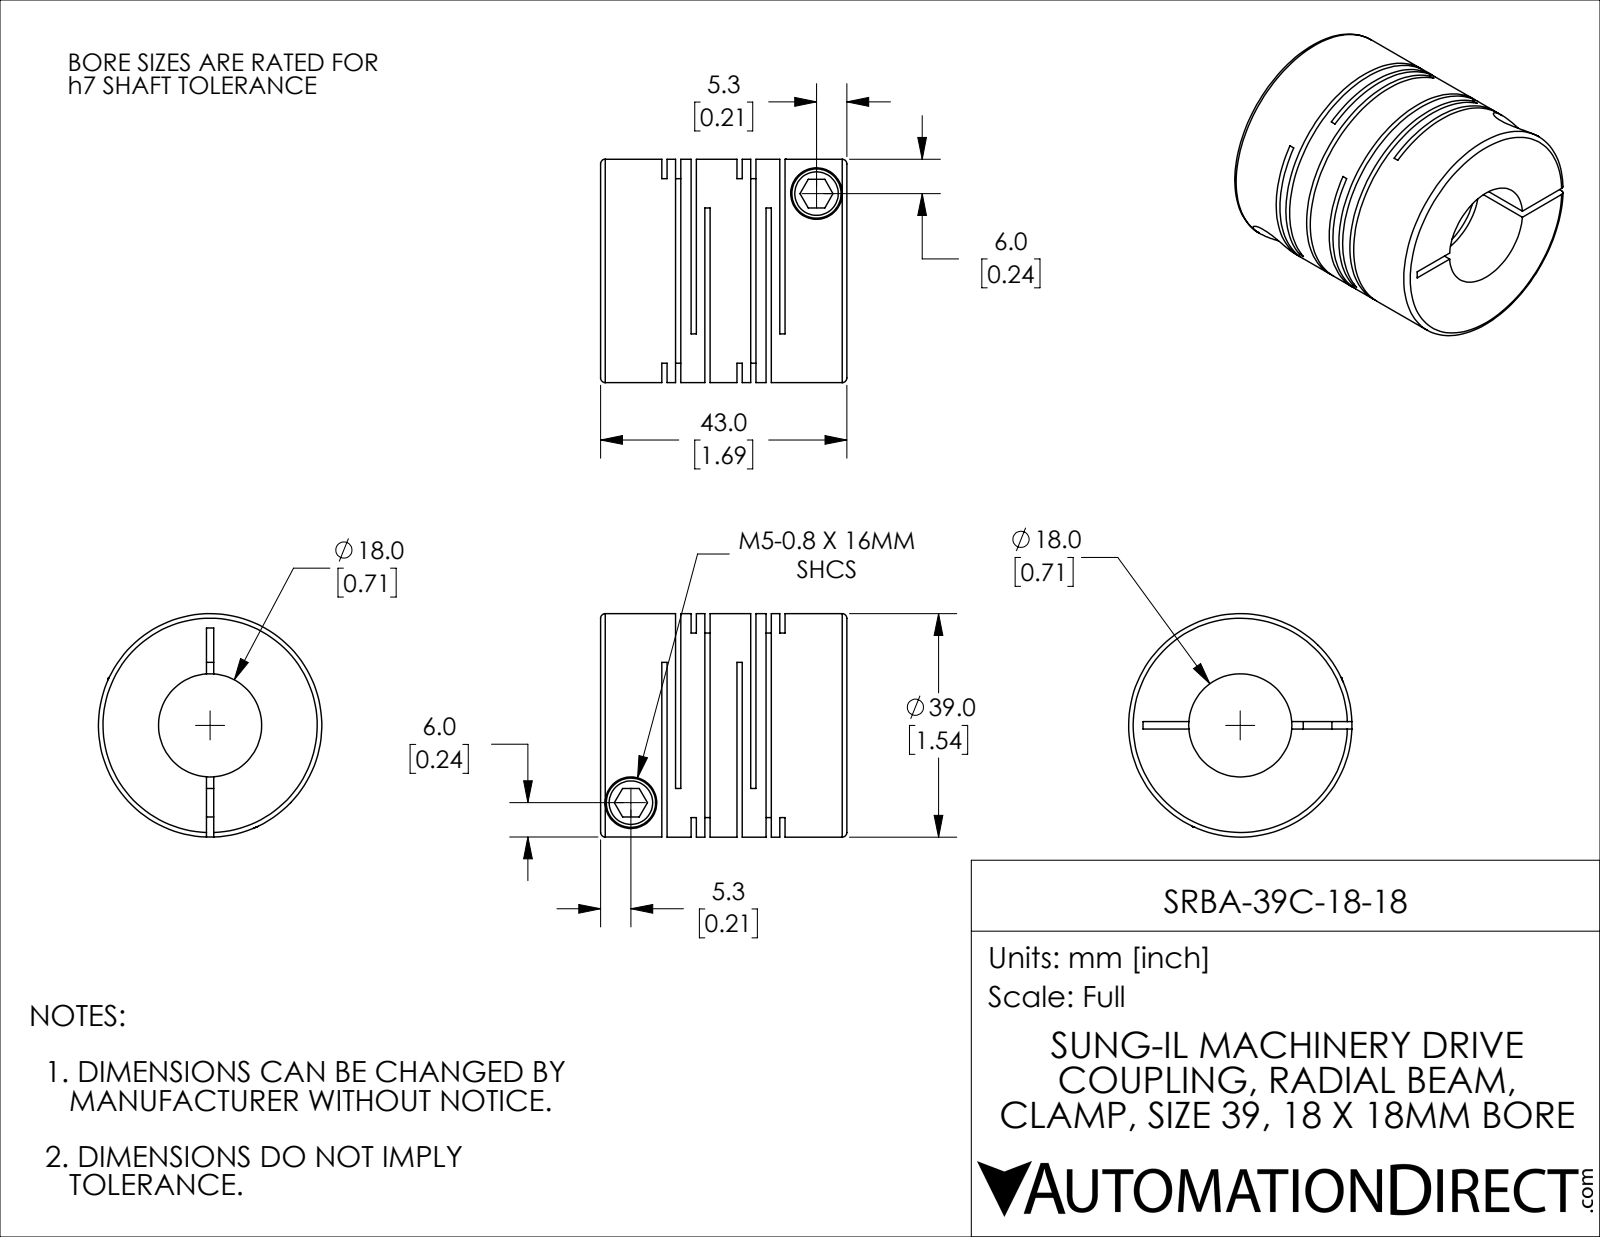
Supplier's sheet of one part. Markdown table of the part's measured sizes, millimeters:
| quantity | value |
| --- | --- |
| part name | SRBA-39C-18-18 |
| STEP written by | SolidWorks 2021 (CONFIG_CONTROL_DESIGN) |
| units | millimeters |
| bodies | 1 solid, 114 faces (60 planar, 42 cylindrical, 12 other) |
| overall size | 43 × 39 × 39 |
| volume | 33 496 mm³ |
| surface area | 22 126 mm² |
| round holes (diameter × count) | 5 × 2, 9 × 2, 18 × 1 |
| round bosses / shafts (diameter × count) | 8.6 × 2, 39 × 1 |
| main face-to-face distances | 13.1, 0.92, 2.4, 5.1, 10.7, 14.02, 18.2, 1.48, 12.18, 4.18 |
